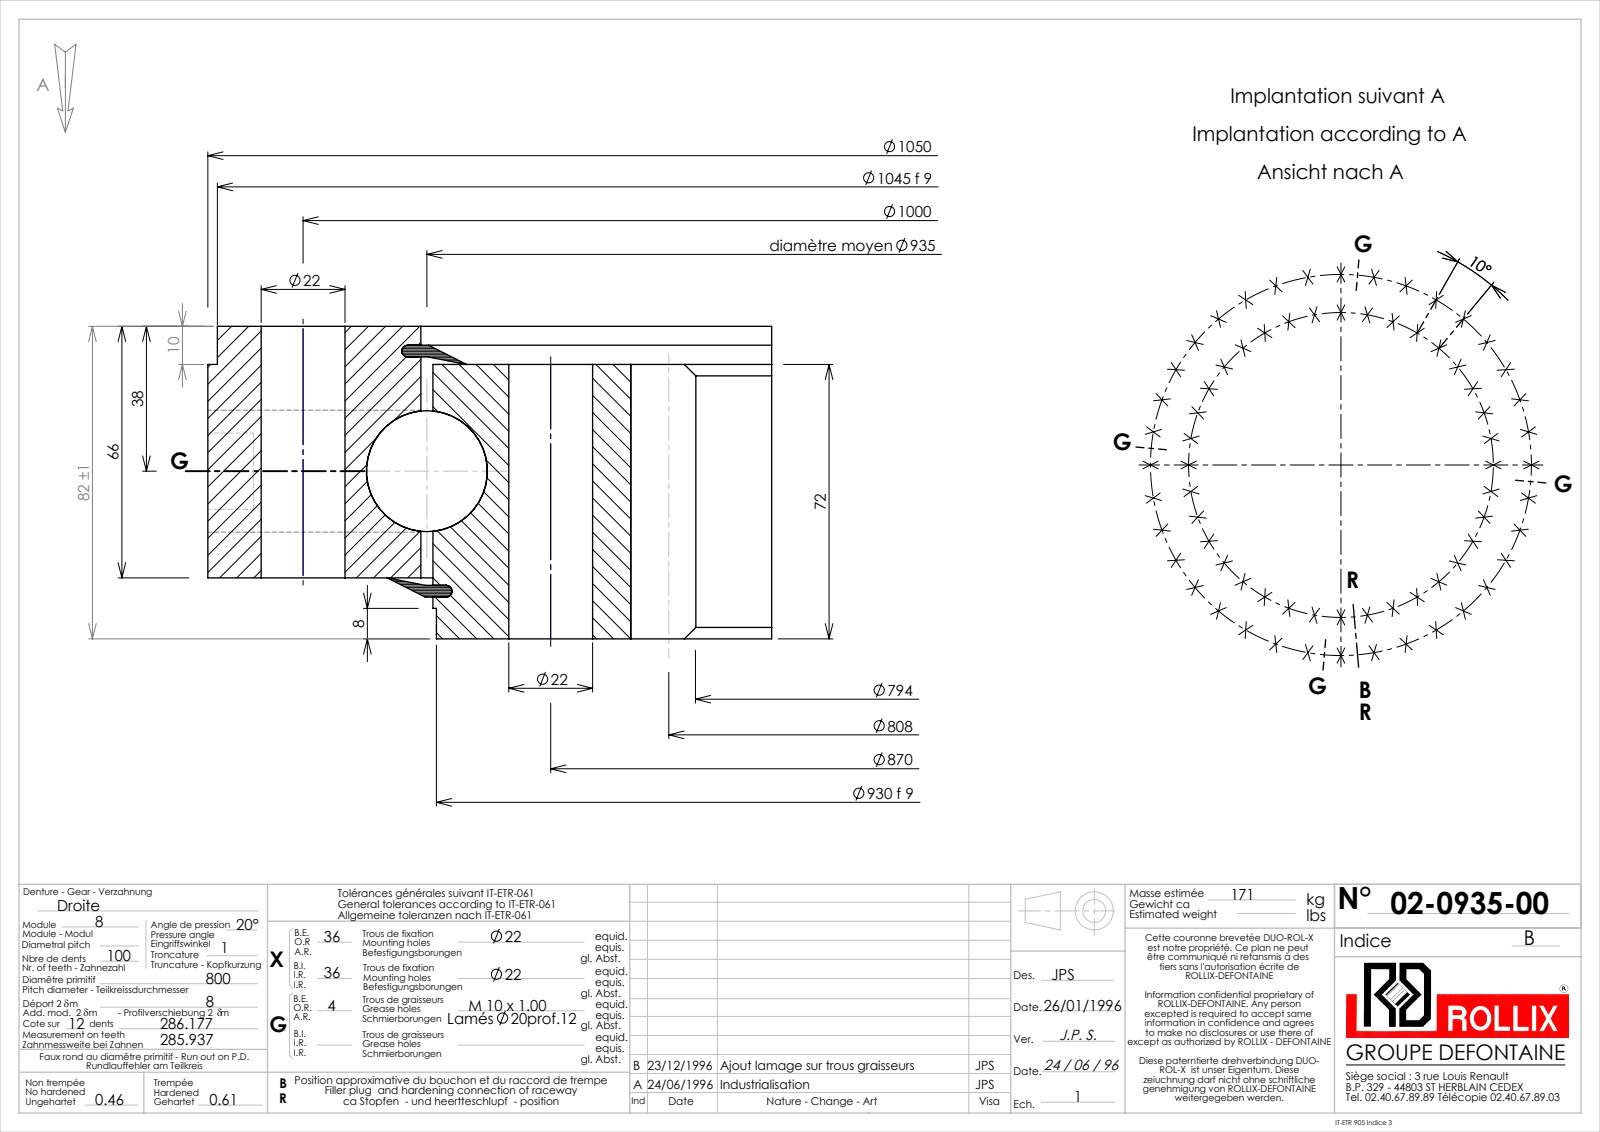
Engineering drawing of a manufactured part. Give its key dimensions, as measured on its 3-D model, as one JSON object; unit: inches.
{"part_name": "02-0935-00", "step_written_by": "SolidWorks 2016 (CONFIG_CONTROL_DESIGN)", "units": "inches", "bodies": {"solids": 5, "faces": 825, "planar": 218, "cylindrical": 379, "other": 228}, "overall_size": [41.339, 41.339, 3.228], "volume_in3": 1199, "surface_area_in2": 3581, "round_holes": [[0.866, 72], [0.354, 4], [0.787, 4], [36.936, 1]], "round_bosses_or_shafts": [[41.339, 1], [41.142, 1], [36.686, 1], [36.614, 1]], "partial_cylinders_radius": [[15.63, 1], [16.299, 1]], "face_to_face_distances": [2.205, 2.598, 0.394, 0.63, 2.835, 3.228, 0.199, 2.404, 0.122, 0.077], "hole_center_spacings": [17.126, 19.646, 26.239, 31.043, 34.122, 11.715, 14.476, 5.948]}
